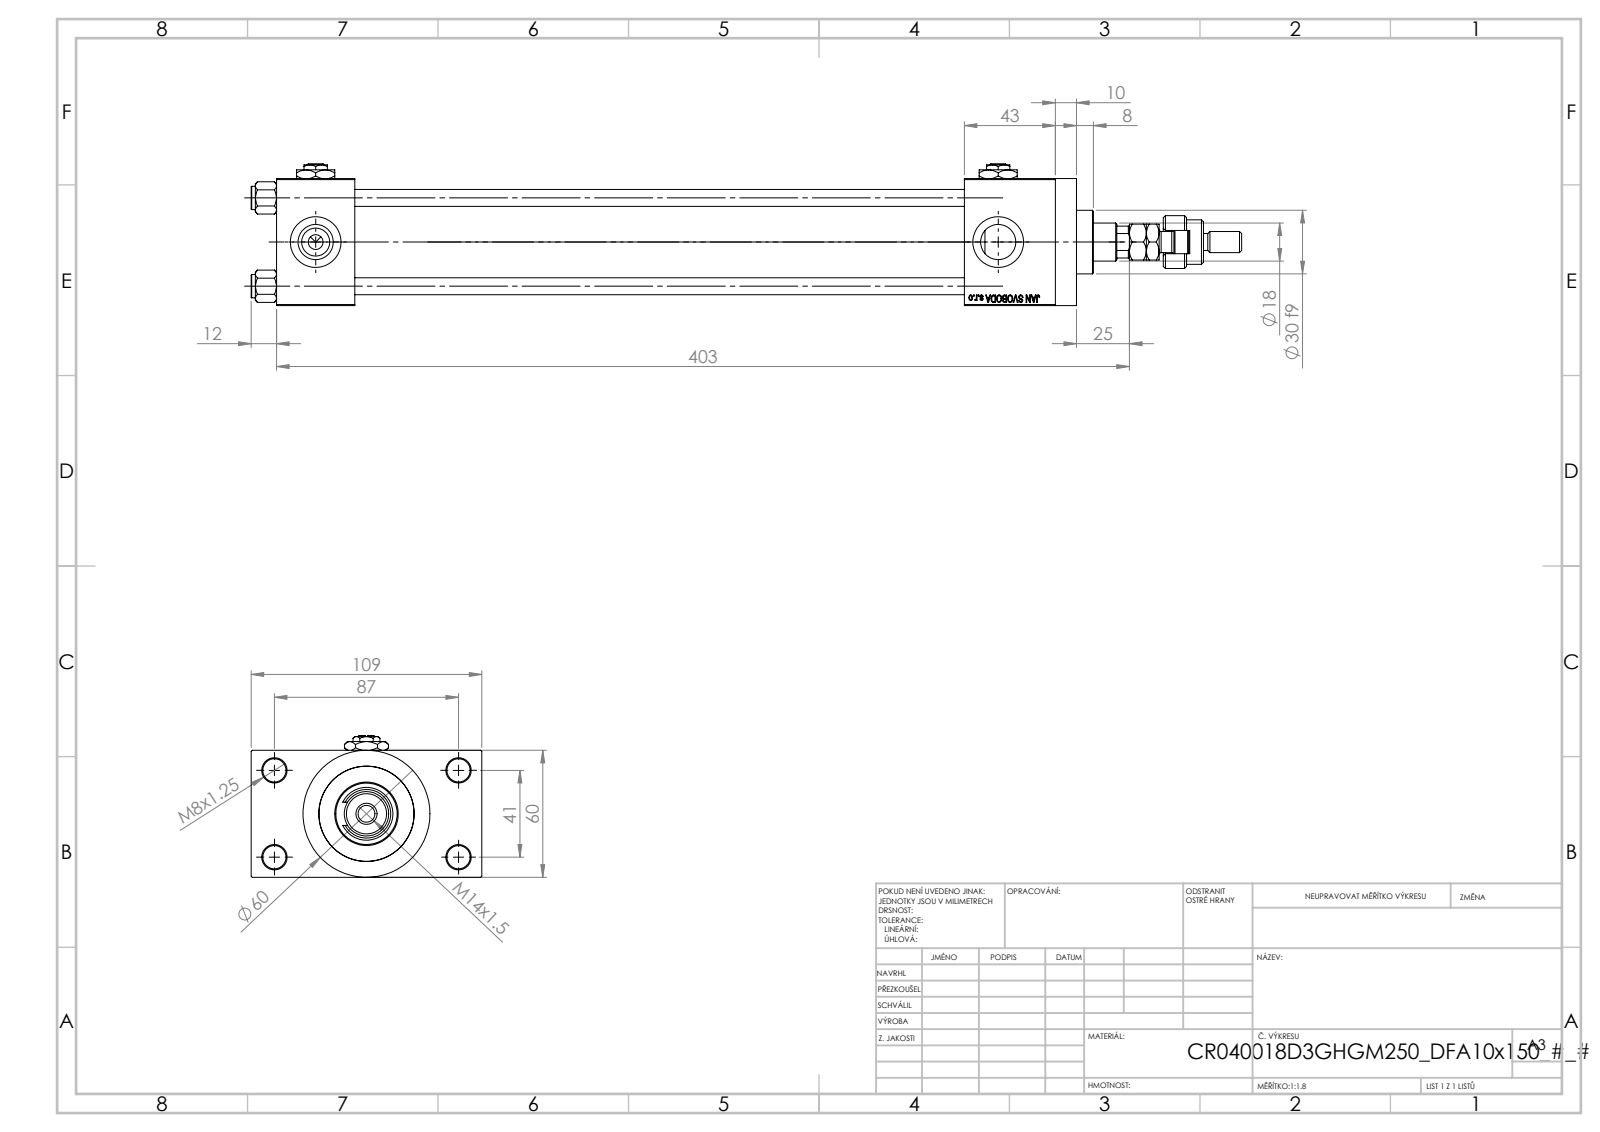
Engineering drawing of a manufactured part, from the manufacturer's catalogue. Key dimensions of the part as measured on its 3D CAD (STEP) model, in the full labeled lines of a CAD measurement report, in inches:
Part name (STEP PRODUCT): V215CR_D_Body; NUT_M5_D; V215CR_VCP_D; MFA (+4 more)
STEP written by: SolidWorks 2019 (CONFIG_CONTROL_DESIGN)
Units: inches
Bodies: 15 solids, 1290 faces (574 planar, 112 cylindrical, 604 other)
Overall size (bounding box): 18.425 × 4.291 × 2.638
Volume: 43.94 in³ · Surface area: 354.8 in²
Round holes (diameter × count): ⌀0.315 ×4, ⌀0.433 ×4, ⌀0.656 ×4, ⌀0.945 ×4, ⌀0.276 ×3, ⌀0.335 ×1, ⌀0.709 ×1, ⌀0.827 ×1, ⌀1.22 ×1, ⌀1.575 ×1, ⌀1.772 ×1
Round bosses / shafts (diameter × count): ⌀0.433 ×4, ⌀2.362 ×1, ⌀1.811 ×1, ⌀1.181 ×1, ⌀0.984 ×1, ⌀0.63 ×1, ⌀0.394 ×1, ⌀0.315 ×1
Partial cylindrical surfaces — rounded edges, fillets, slot ends (radius × count): R0.217 ×1, R0.335 ×1, R0.344 ×1
Main face-to-face distances: 2.362, 0.965, 11.339, 3.327, 1.457, 12.795, 1.693, 14.488, 13.031, 2.087
Hole centre spacings: 0.892, 1.161, 1.642, 1.856, 1.893, 2.533, 3.011, 1.614
